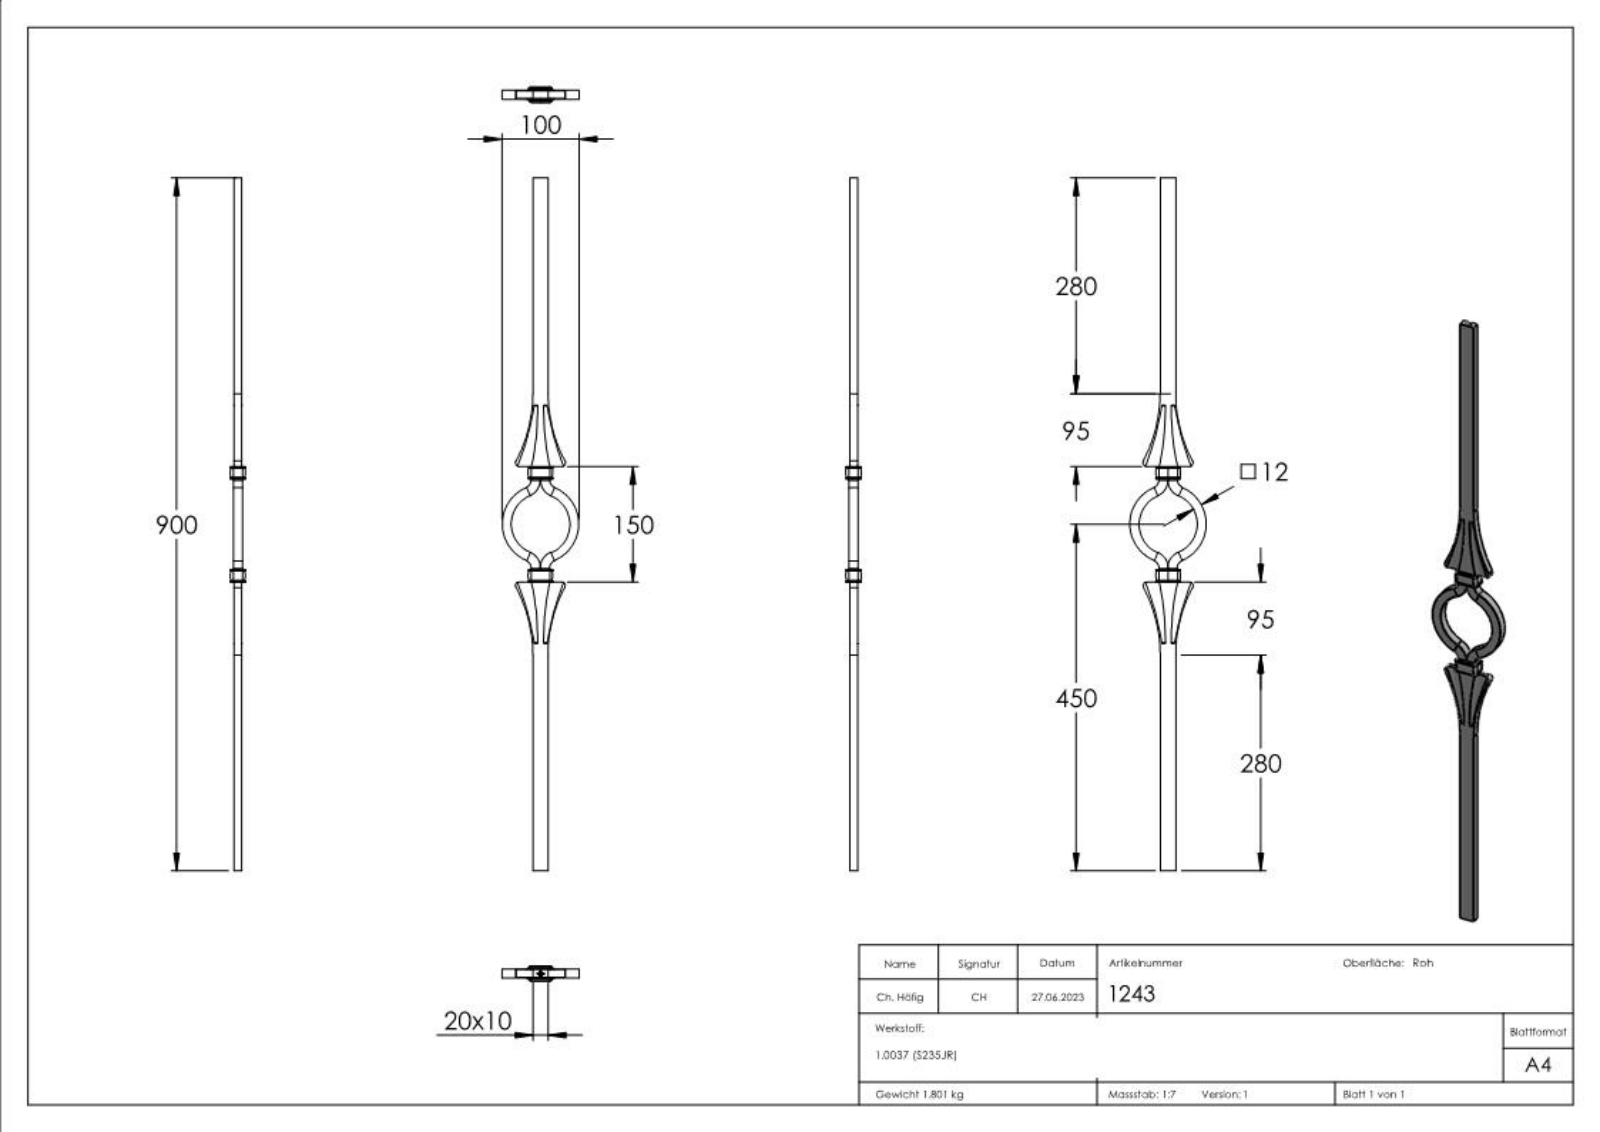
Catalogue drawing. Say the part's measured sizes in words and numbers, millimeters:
The part is named "1243". Its 3-D file was written by "SolidWorks 2018 (CONFIG_CONTROL_DESIGN)". It is 2 solids with 597 faces: 287 planar, 134 cylindrical and 176 other. Overall it measures 900 by 100 by 20 millimeters. Its volume is 230 853 cubic millimeters and its surface area 77 427 square millimeters. Partial cylindrical surfaces (rounded edges, fillets, slot ends): 48 of radius 0.5, 16 of radius 0.2, 8 of radius 21.62, 4 of radius 1, 4 of radius 4, 4 of radius 5, 4 of radius 10, 4 of radius 21.95. The main face-to-face distances are 10, 1, 11, 12, 20, 2, 13, 10.05, 11.95, 12.05.
